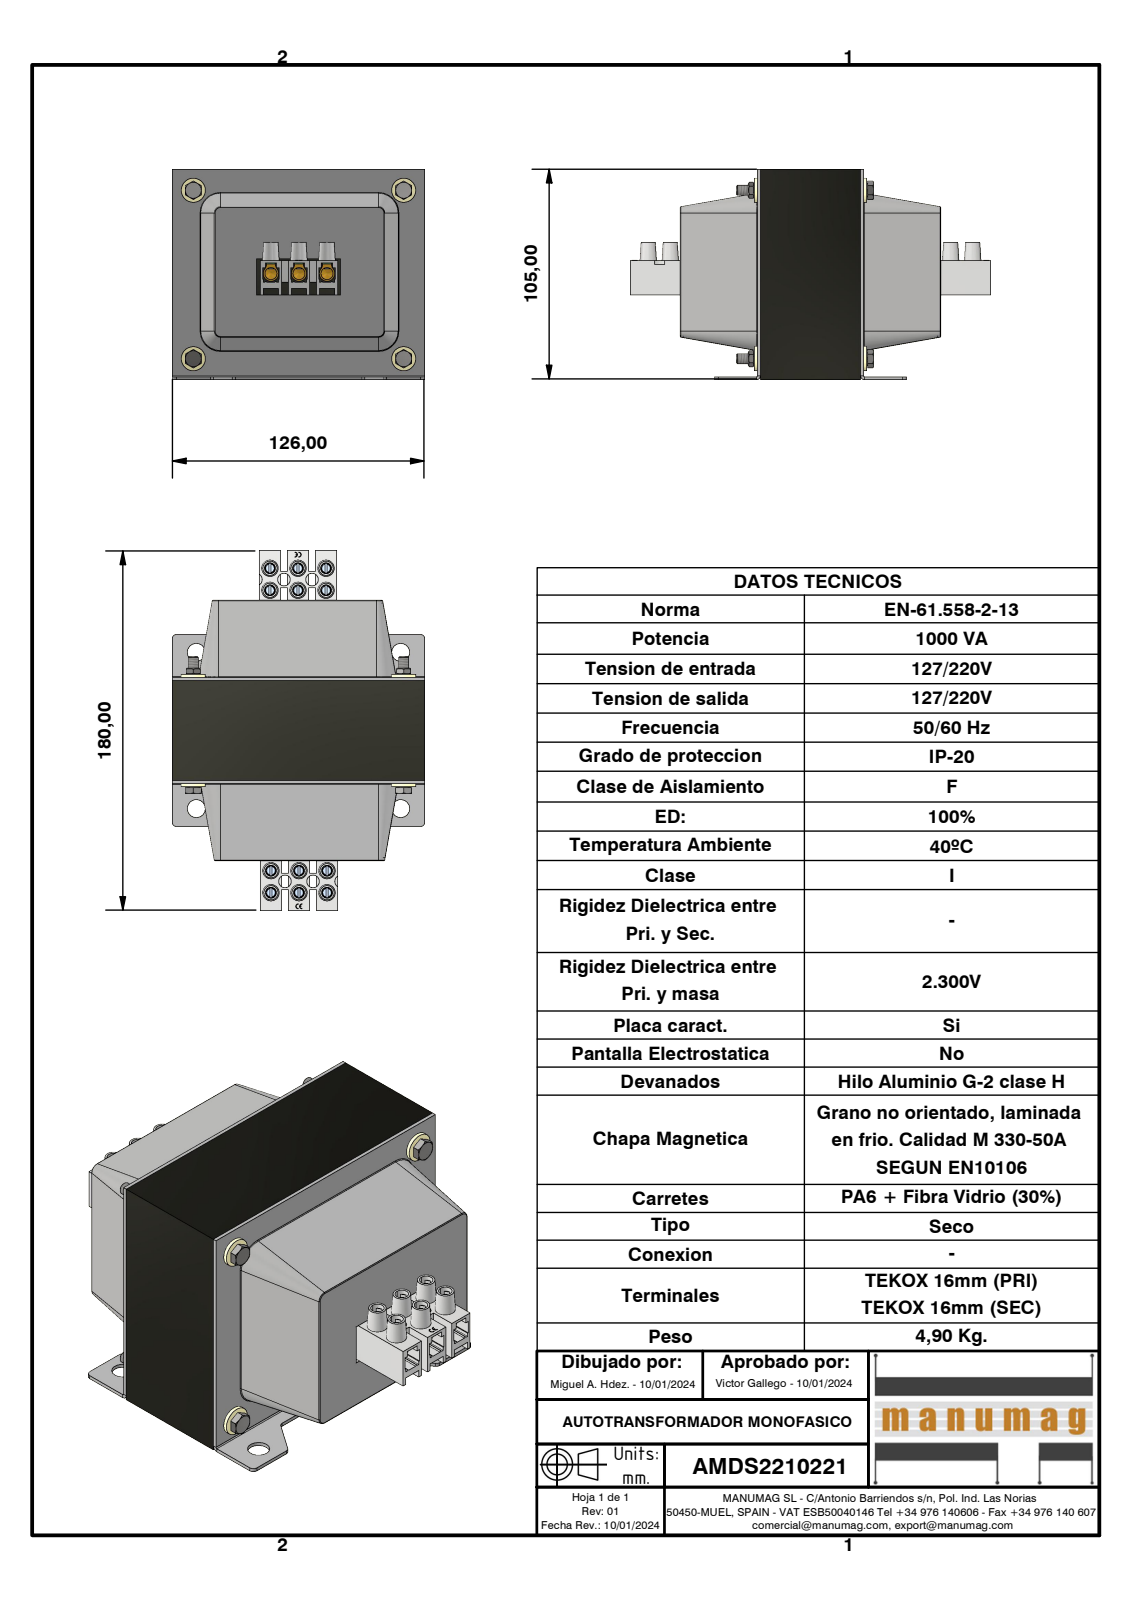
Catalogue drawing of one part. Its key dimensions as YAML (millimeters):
part_name: "AMDS2210221; centrador M5; DIN 933 - M5 x 65; DIN 934 - M4 x 0,7 (+8 more)"
step_written_by: "Autodesk Inventor 2023 (AUTOMOTIVE_DESIGN)"
units: millimeters
bodies: {solids: 51, faces: 2186, planar: 1484, cylindrical: 282, other: 420}
overall_size: [180, 126, 105]
volume: 590654
surface_area: 203176
round_holes:
  - {diameter: 3.24, count: 16}
  - {diameter: 5.5, count: 12}
  - {diameter: 6, count: 10}
  - {diameter: 5, count: 4}
  - {diameter: 6.3, count: 4}
  - {diameter: 6.5, count: 4}
  - {diameter: 9, count: 4}
round_bosses_or_shafts:
  - {diameter: 4, count: 12}
  - {diameter: 12, count: 4}
  - {diameter: 6.7, count: 4}
  - {diameter: 5.9, count: 4}
  - {diameter: 4.57, count: 4}
partial_cylinders:
  - {radius: 2.75, count: 24}
  - {radius: 0.38, count: 16}
  - {radius: 0.82, count: 16}
  - {radius: 2, count: 14}
  - {radius: 3, count: 12}
  - {radius: 0.81, count: 8}
  - {radius: 0.1, count: 6}
  - {radius: 0.22, count: 6}
face_to_face_distances: [1.5, 38.5, 90, 21, 50, 84, 105, 37, 51.5, 40]
hole_center_spacings: [14, 8.8, 9, 17.8, 11, 28, 151, 21.67]
